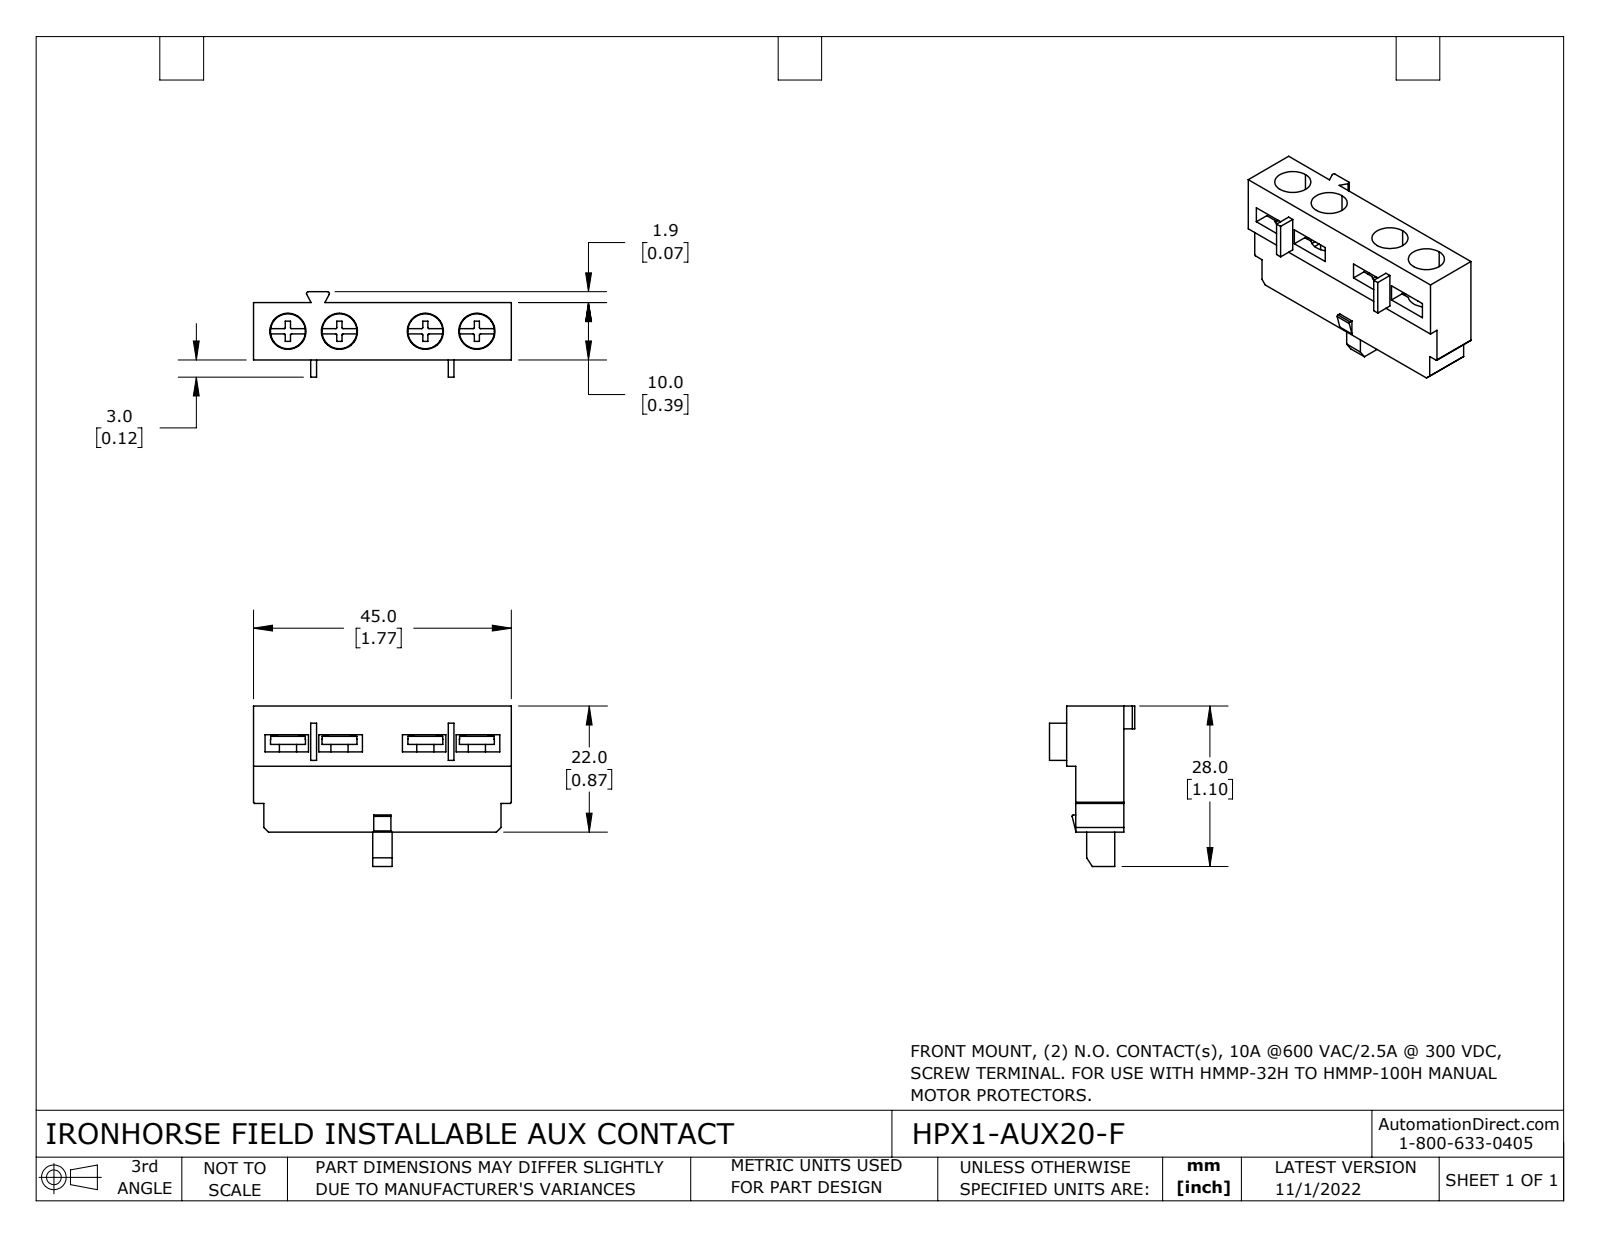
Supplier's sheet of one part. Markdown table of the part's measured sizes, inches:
| quantity | value |
| --- | --- |
| part name | HPX1-AUX20-F |
| STEP written by | SolidWorks 2021 (CONFIG_CONTROL_DESIGN) |
| units | inches |
| bodies | 5 solids, 249 faces (190 planar, 51 cylindrical, 8 other) |
| overall size | 2.085 × 1.102 × 0.786 |
| volume | 1.31 in³ |
| surface area | 18.05 in² |
| round holes (diameter × count) | 0.118 × 4, 0.24 × 4, 0.248 × 4 |
| partial cylindrical surfaces (radius × count) | 0.008 × 19, 0.012 × 2, 0.02 × 2 |
| main face-to-face distances | 0.039, 0.291, 0.354, 0.394, 0.331, 0.252, 0.063, 0.102, 0.866, 0.197 |
| hole center spacings | 0.354, 0.945, 0.591, 1.299 |
